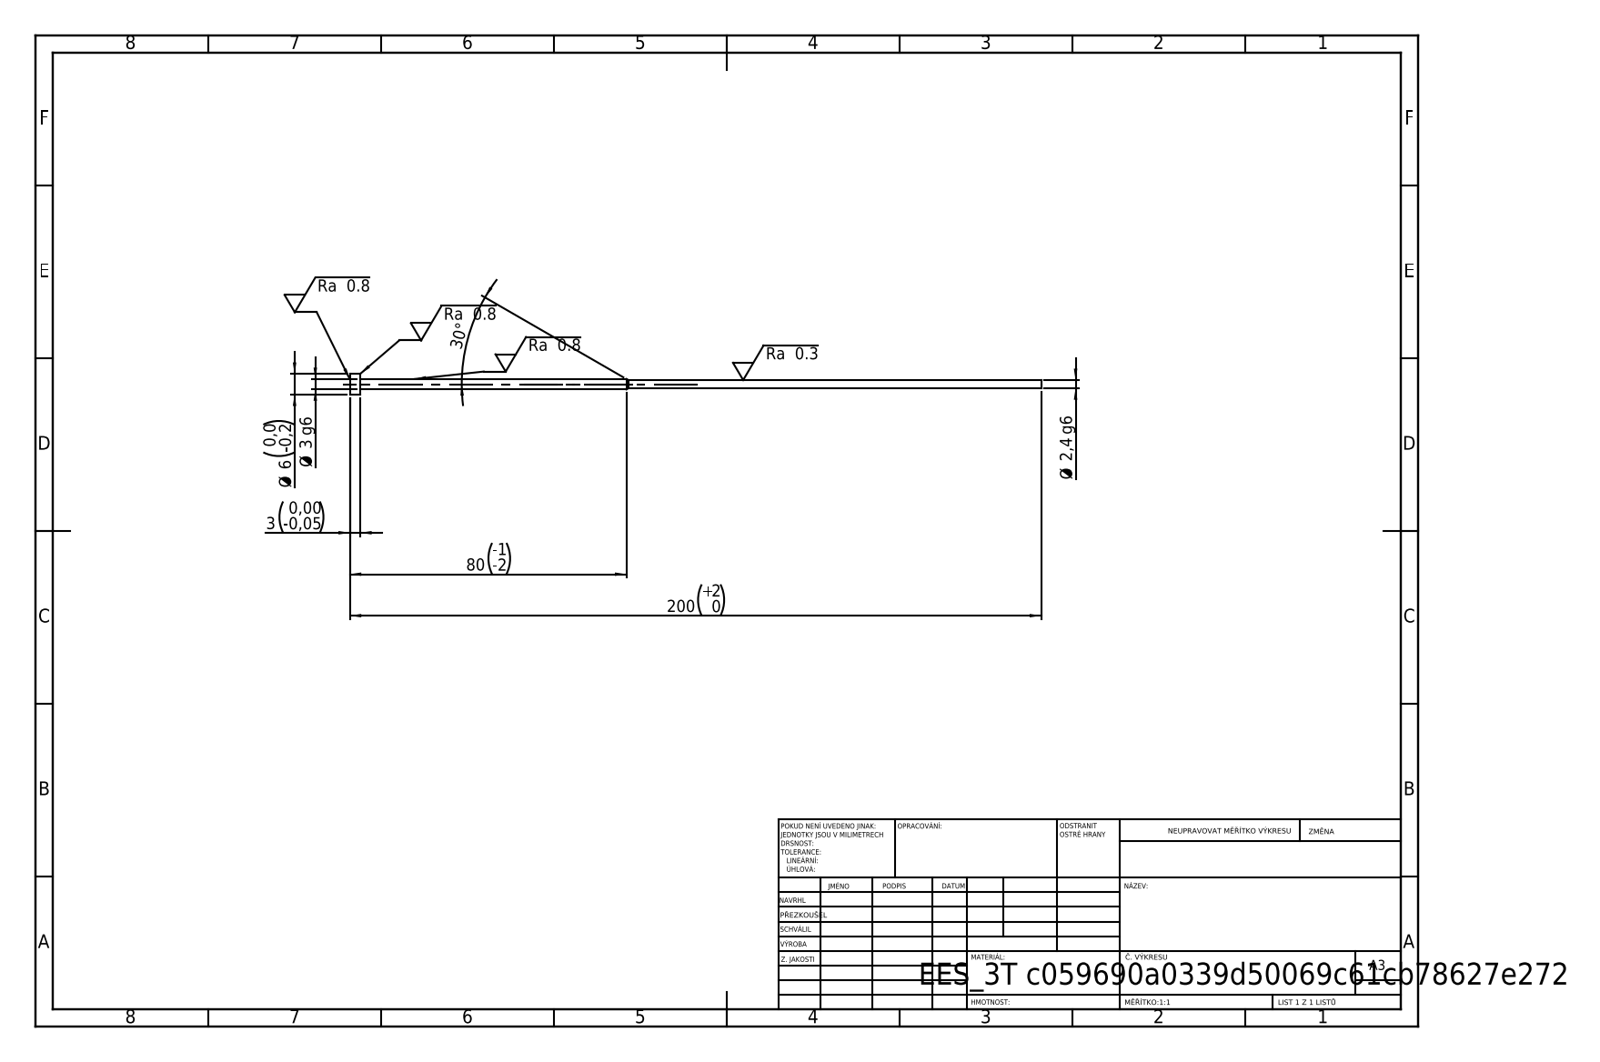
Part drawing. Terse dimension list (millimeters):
written by: SolidWorks 2019 (CONFIG_CONTROL_DESIGN)
unit: mm
bodies: 1 solid, 11 faces (3 planar, 6 cylindrical, 2 other)
size: 200 × 6 × 6
volume: 1 173 mm³; area: 1 742 mm²
bosses: 1× ⌀6, 1× ⌀3, 1× ⌀2.4
face distances: 3, 197, 200
